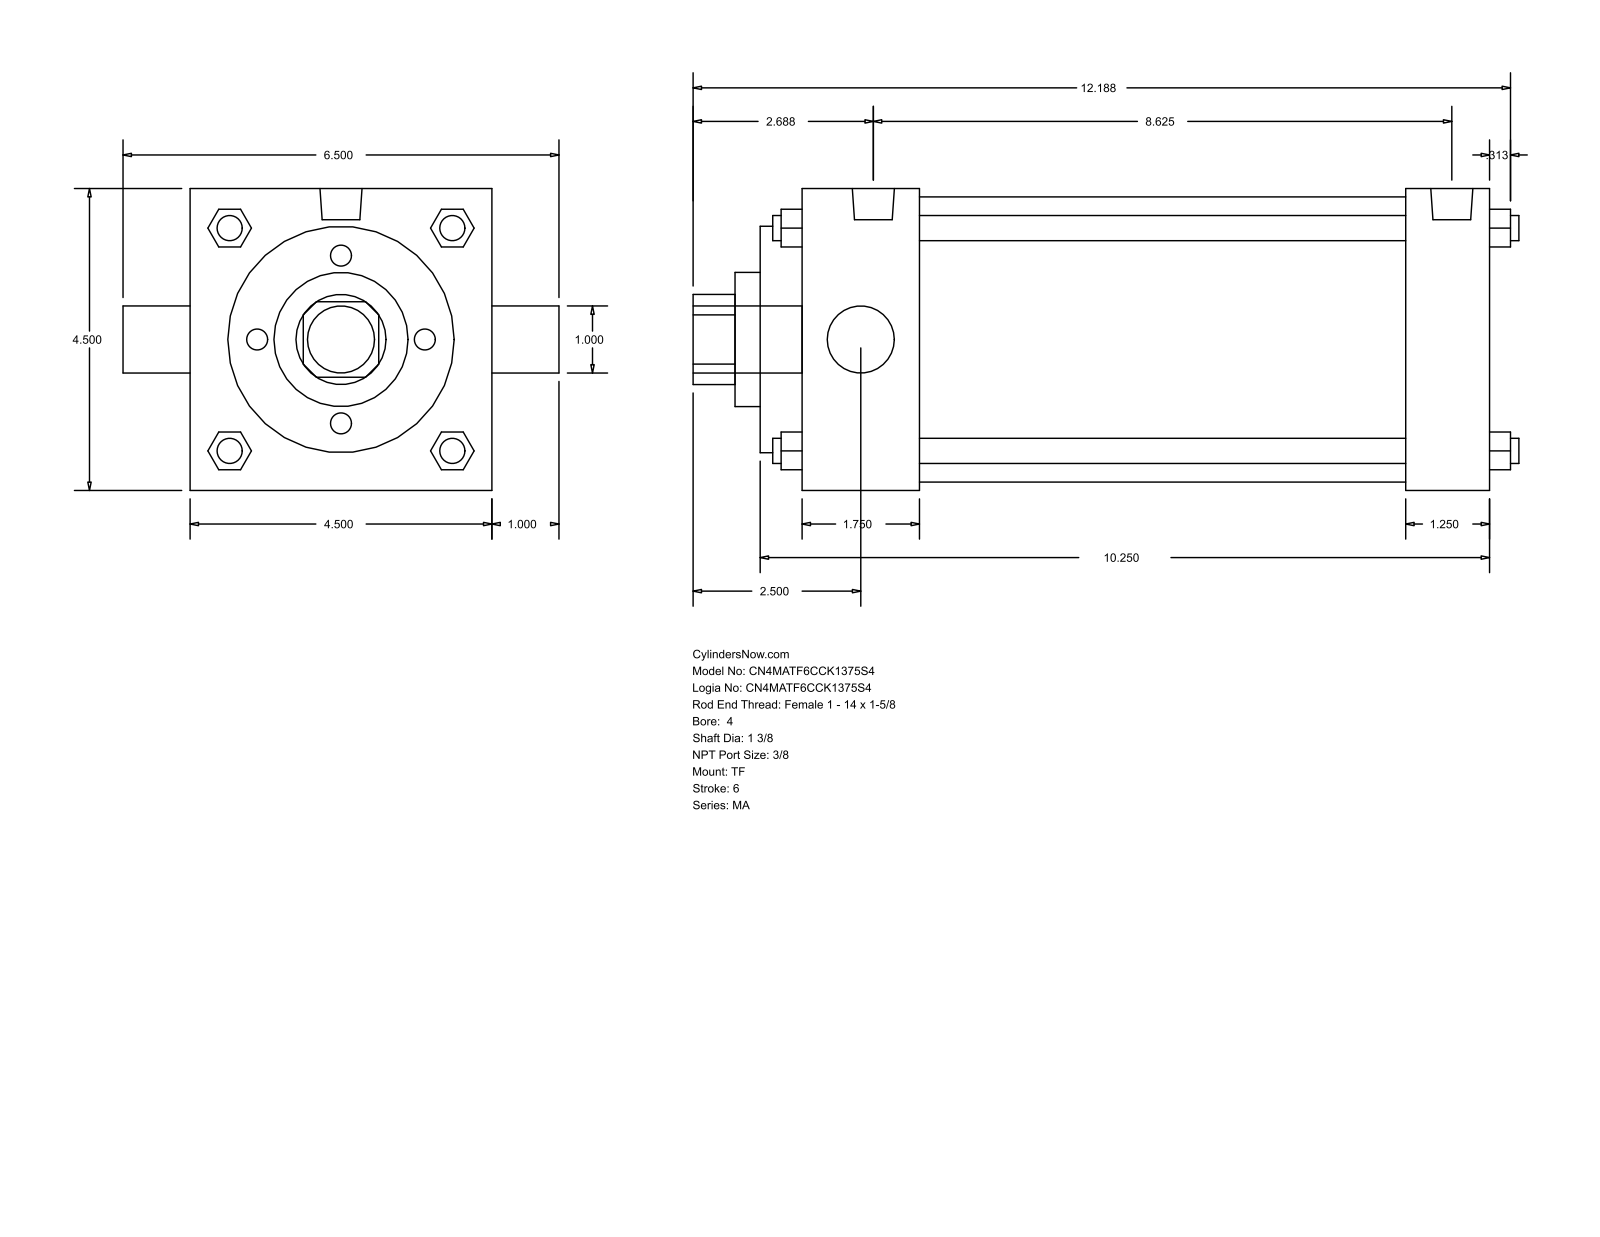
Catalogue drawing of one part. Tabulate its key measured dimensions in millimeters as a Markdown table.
| quantity | value |
| --- | --- |
| part name | MA_TF__0400_1.375 |
| STEP written by | GSSL Pune (CONFIG_CONTROL_DESIGN) |
| units | millimeters |
| bodies | 0 solids, 122 faces (93 planar, 29 cylindrical, 0 other) |
| overall size | 312.74 × 165.1 × 114.3 |
| round holes (diameter × count) | 25.4 × 1, 34.92 × 1, 50.8 × 1, 85.72 × 1, 107.95 × 1 |
| round bosses / shafts (diameter × count) | 9.53 × 4, 11.11 × 3, 15.93 × 2, 25.4 × 1 |
| partial cylindrical surfaces (radius × count) | 17.06 × 1 |
| main face-to-face distances | 114.3, 260.35, 276.22, 15.87, 244.48, 228.61, 31.74, 60.32, 44.45, 184.16 |
